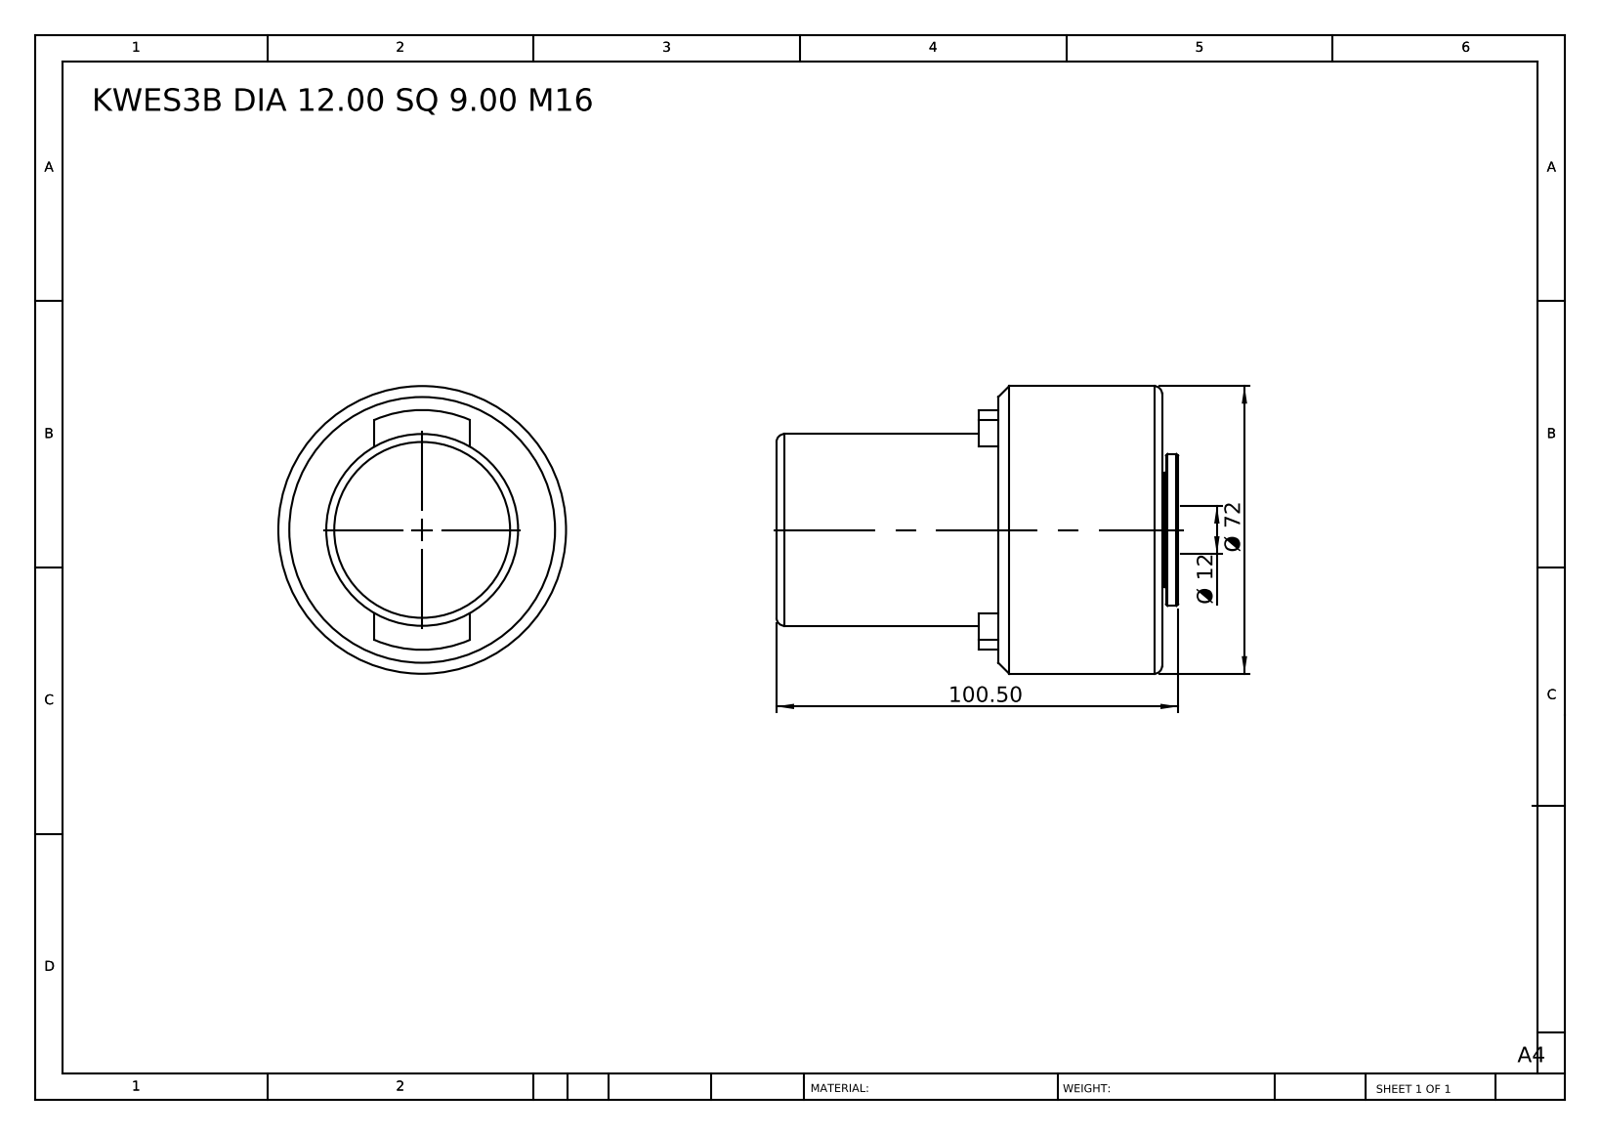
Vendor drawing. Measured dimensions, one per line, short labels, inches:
name: KWES3B DIA 12.00 SQ 9.00 3-8'''''''' BSPT
written by: SolidWorks 2014 (CONFIG_CONTROL_DESIGN)
unit: in
bodies: 1 solid, 39 faces (12 planar, 13 cylindrical, 14 other)
size: 3.957 × 2.835 × 2.835
volume: 16.31 in³; area: 43.53 in²
holes: 1× ⌀0.472
bosses: 1× ⌀2.835, 1× ⌀1.89, 1× ⌀1.496, 1× ⌀1.122
rounds: 1× R1.181
face distances: 3.799, 2.185, 1.614, 3.957, 1.772, 0.157, 3.839, 1.654, 0.039, 0.118
